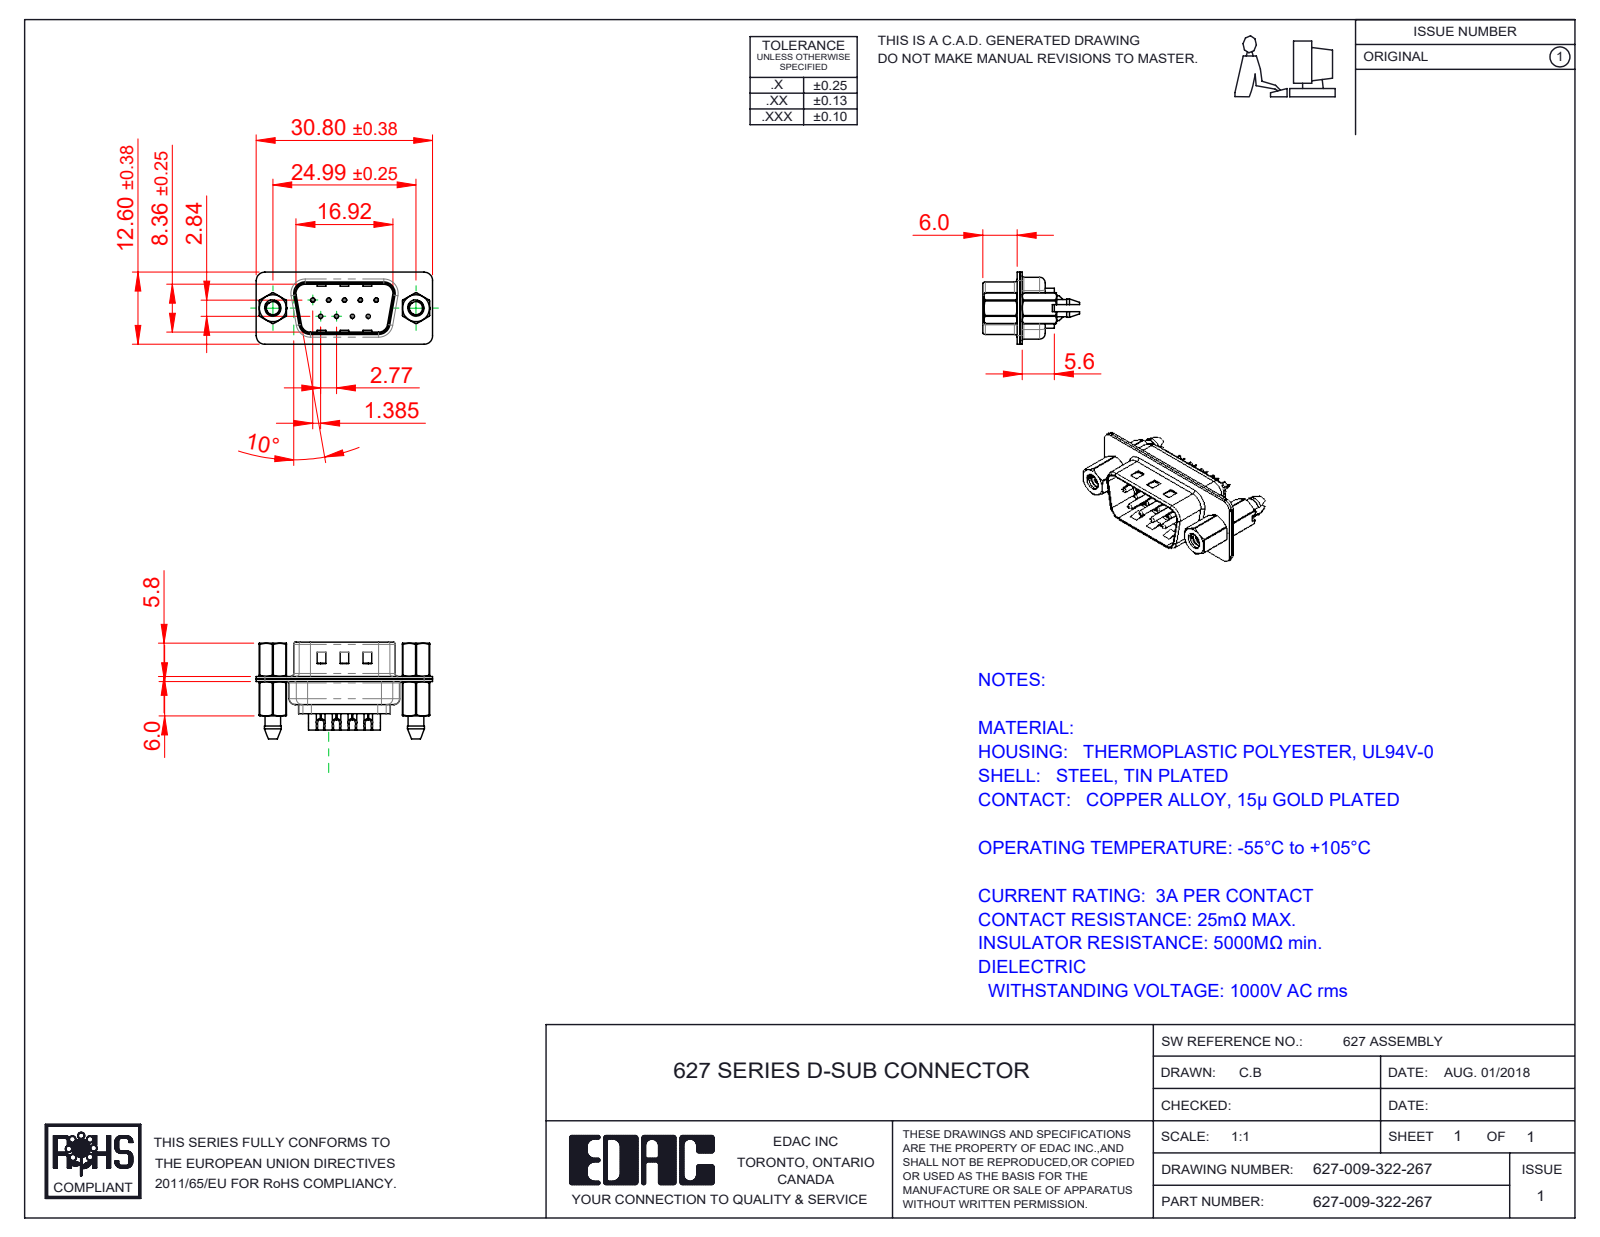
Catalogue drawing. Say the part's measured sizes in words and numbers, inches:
The part is named "627 Contact Row 1_22L; 627 4-40 Hex Standoff; 627 Contact Row 2_22L; 627 4-40 Threaded Boardlock_LP (+4 more)". Its 3-D file was written by "SolidWorks 2020 (CONFIG_CONTROL_DESIGN)". It is 16 solids with 1080 faces: 287 planar, 494 cylindrical and 299 other. Overall it measures 1.213 by 0.665 by 0.496 inches. Its volume is 0.1 cubic inches and its surface area 7.327 square inches. Round holes: 9 of diameter 0.014, 9 of diameter 0.043, 9 of diameter 0.063, 2 of diameter 0.089, 2 of diameter 0.09, 2 of diameter 0.157, 2 of diameter 0.189. Round bosses or shafts: 9 of diameter 0.079, 9 of diameter 0.059, 9 of diameter 0.03, 2 of diameter 0.193, 2 of diameter 0.11. Partial cylindrical surfaces (rounded edges, fillets, slot ends): 20 of radius 0.059, 12 of radius 0.079, 10 of radius 0.063, 8 of radius 0.02, 6 of radius 0.039, 4 of radius 0.01, 4 of radius 0.024, 4 of radius 0.026. The main face-to-face distances are 0.018, 0.016, 0.035, 0.032, 0.377, 0.055, 0.187, 0.345, 0.256, 0.02. The hole center spacings are 0.124, 0.109, 0.218, 0.198, 0.198, 0.327, 0.294, 0.295.
